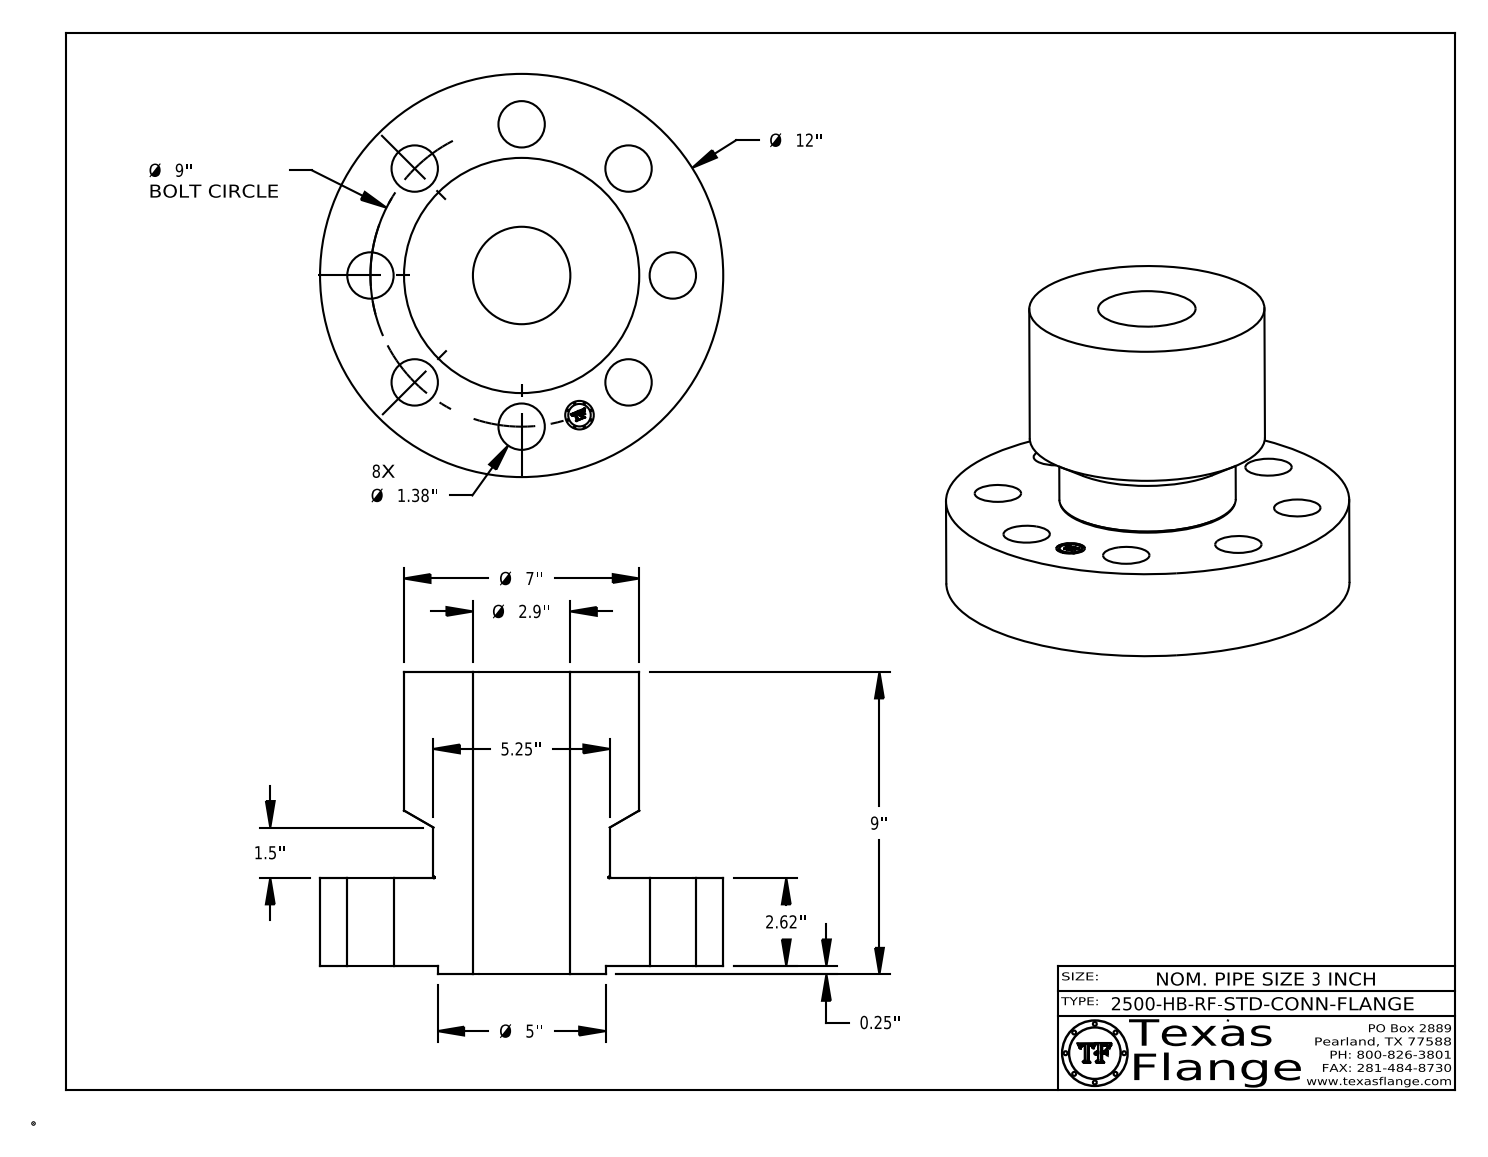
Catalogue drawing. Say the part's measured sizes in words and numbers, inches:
The part is named "3-2500-HB-RF-STD-CONN-FLANGE". Its 3-D file was written by "CATIA V5 STEP AP214 (AUTOMOTIVE_DESIGN)". It is 1 solid with 421 faces: 369 planar, 46 cylindrical and 6 other. Overall it measures 12 by 12 by 9 inches. Its volume is 416.6 cubic inches and its surface area 617 square inches. Round holes: 8 of diameter 1.38, 1 of diameter 0.85, 1 of diameter 2.9. Round bosses or shafts: 8 of diameter 0.051, 1 of diameter 12, 1 of diameter 7, 1 of diameter 5.25, 1 of diameter 5, 1 of diameter 0.67. The main face-to-face distances are 2.62, 8.75, 6.13, 0.25, 2.87, 9, 2.865, 2.615, 6.135, 0.254. The hole center spacings are 4.5, 3.444, 6.364, 8.315, 1.756, 5, 7.483, 9.
